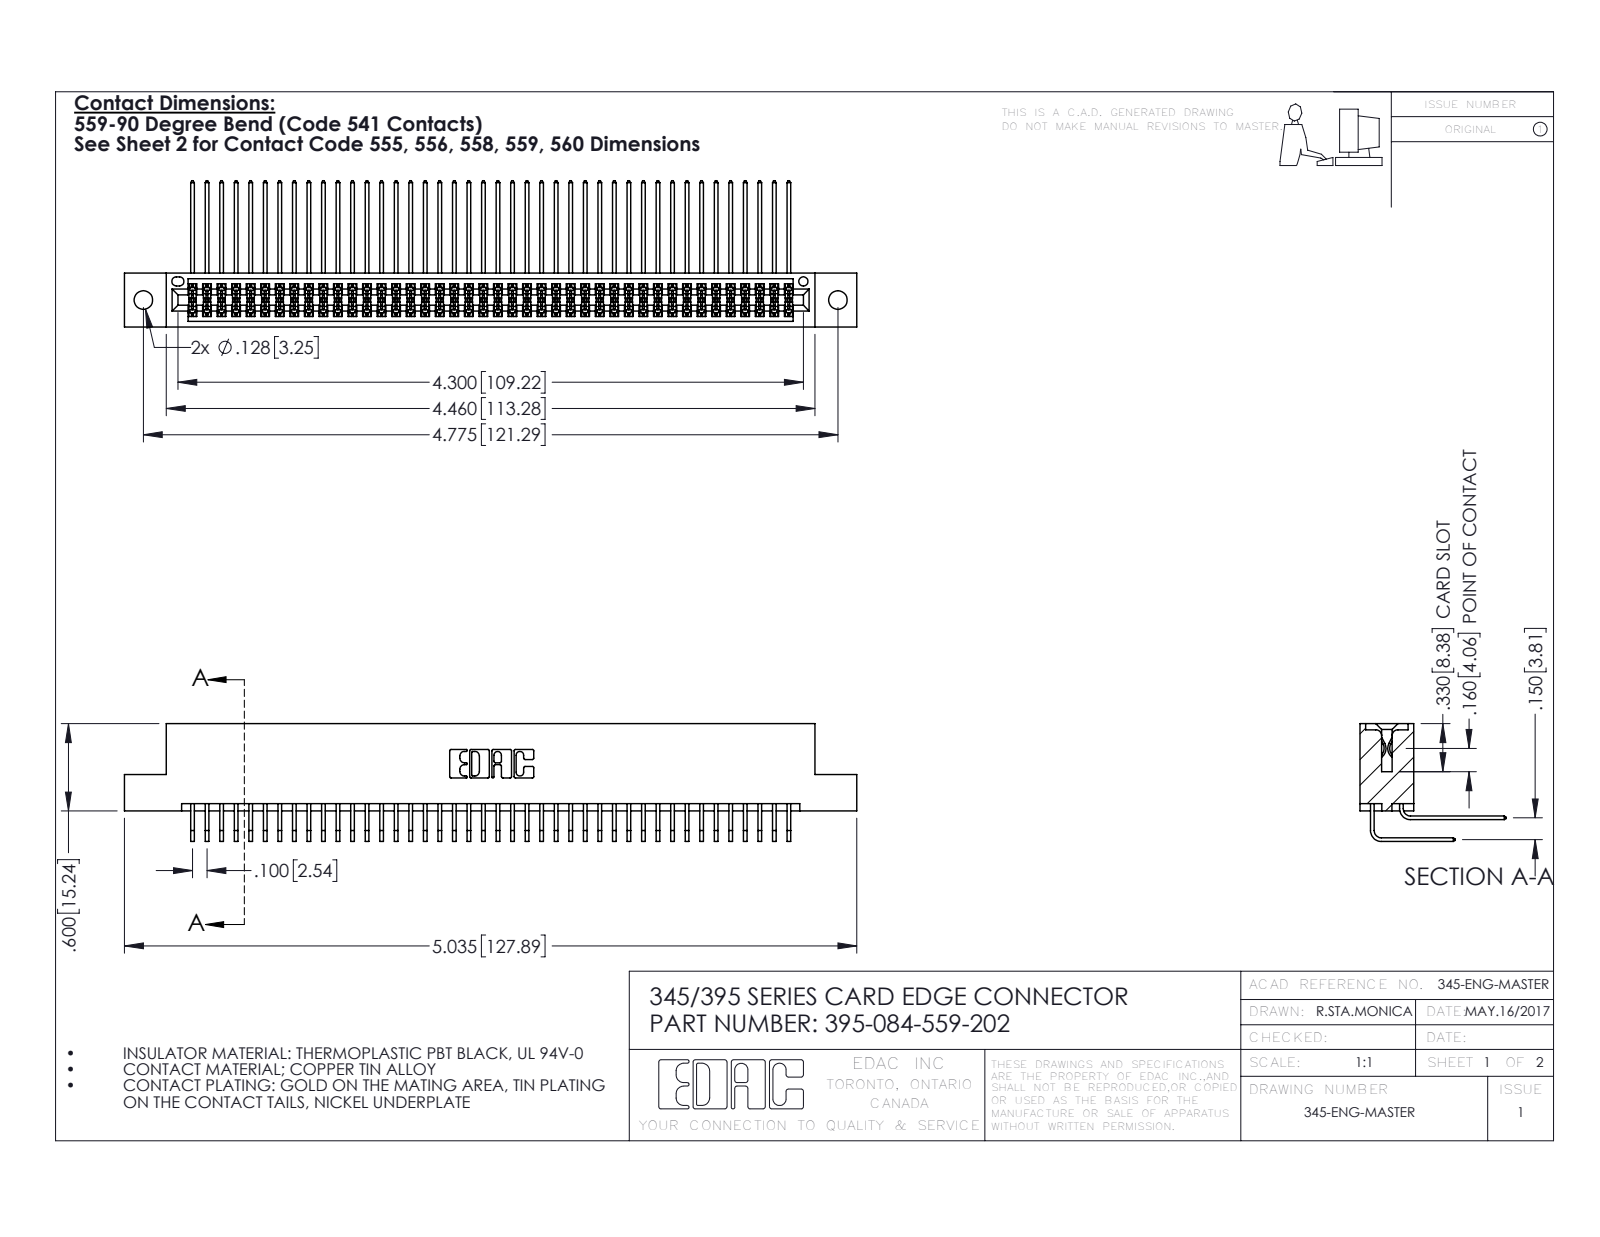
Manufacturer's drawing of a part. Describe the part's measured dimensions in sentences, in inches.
The part is named "395-084-559-202; 345 Part_Flush Mounting Lugs - 0.128 Dia; 345-292-001_558 559 Tail - 1; 345-292-001_559 Tail - 2". Its 3-D file was written by "SolidWorks 2016 (CONFIG_CONTROL_DESIGN)". It is 85 solids with 4494 faces: 3020 planar, 1474 cylindrical and 0 other. Overall it measures 5.035 by 1.005 by 0.809 inches. Its volume is 0.785 cubic inches and its surface area 32.6 square inches. Round holes: 2 of diameter 0.128, 1 of diameter 0.064. Partial cylindrical surfaces (rounded edges, fillets, slot ends): 127 of radius 0.006, 22 of radius 0.01, 6 of radius 0.007, 6 of radius 0.031, 3 of radius 0.026, 2 of radius 0.014, 2 of radius 0.019, 2 of radius 0.022. The main face-to-face distances are 0.072, 0.298, 0.2, 0.37, 0.098, 0.272, 0.025, 0.225, 0.175, 0.15. The hole center spacings are 0.27, 4.539, 4.775.
